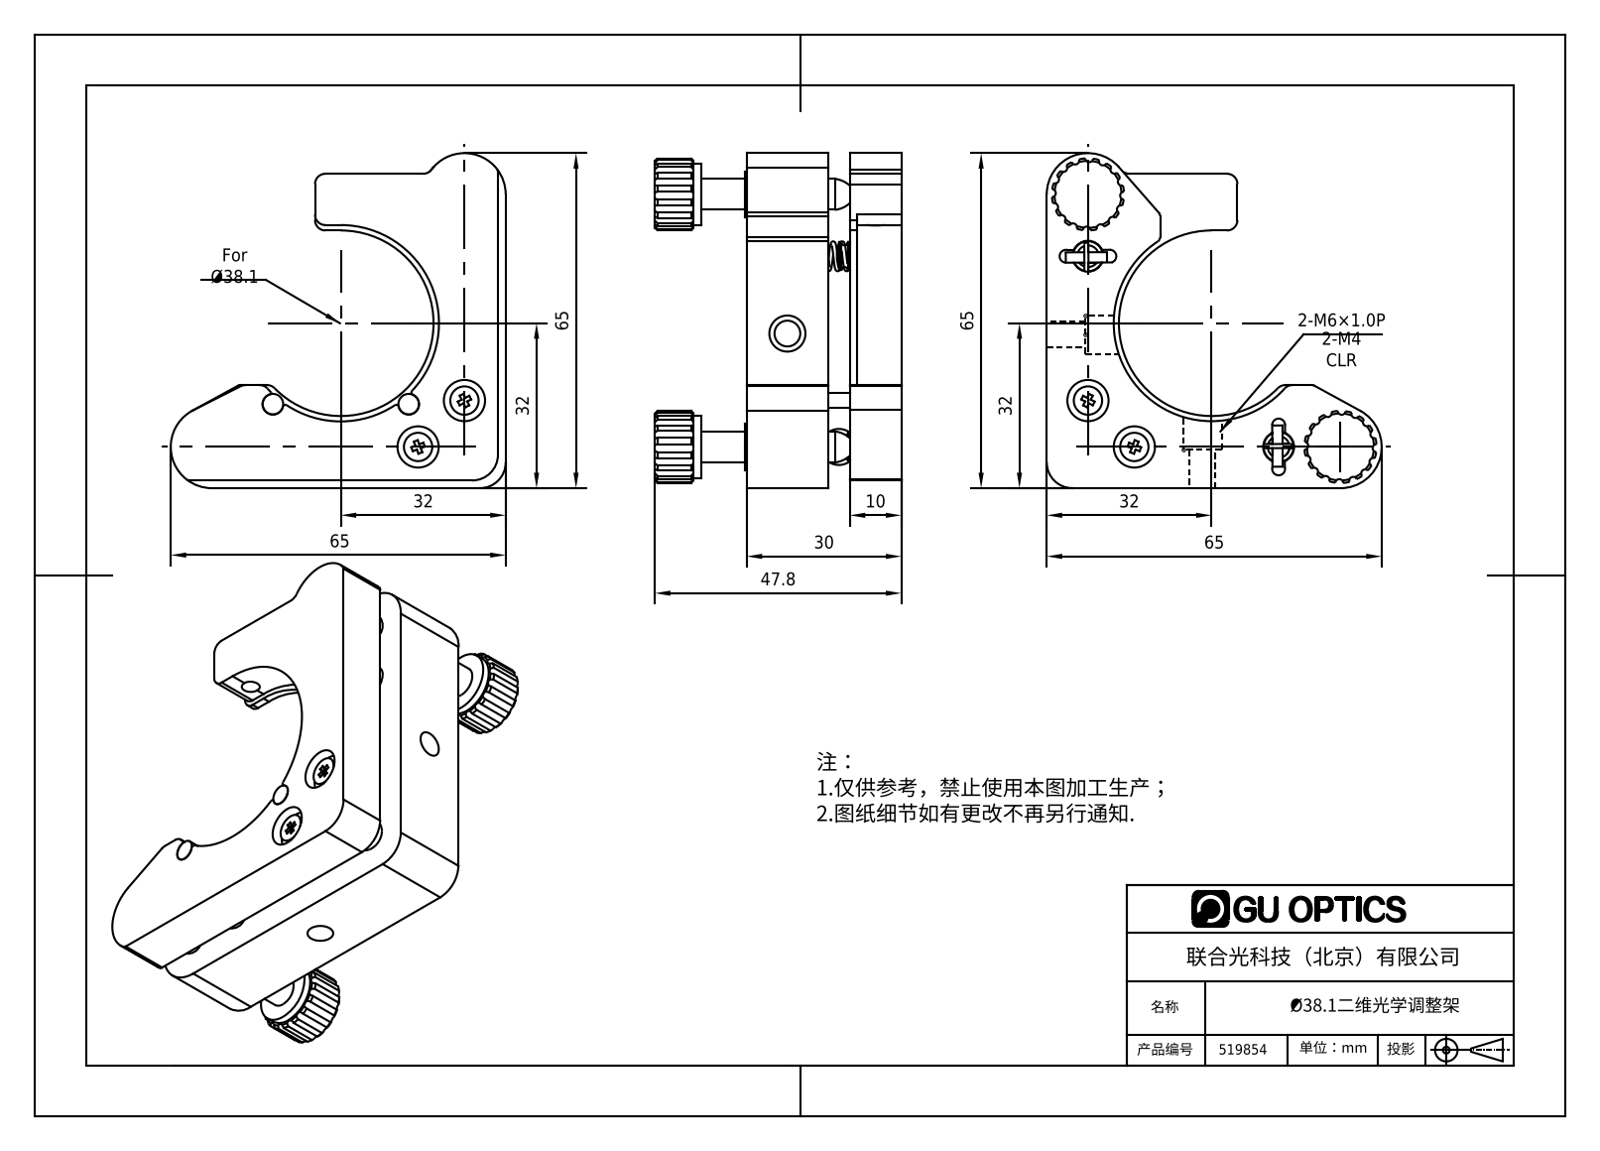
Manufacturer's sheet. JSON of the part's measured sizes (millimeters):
{"part_name": "519854", "step_written_by": "SolidWorks 2016 (AUTOMOTIVE_DESIGN)", "units": "millimeters", "bodies": {"solids": 0, "faces": 628, "planar": 220, "cylindrical": 203, "other": 205}, "overall_size": [65, 65, 47.8], "round_holes": [[6, 4], [8, 4], [4, 3], [5, 2], [7, 2], [3.5, 1]], "round_bosses_or_shafts": [[12, 2], [9, 2], [5.4, 2], [3, 2], [2, 2], [0.8, 2], [4, 1]], "partial_cylinders_radius": [[0.75, 32], [2, 8], [1, 5], [1.25, 4], [0.5, 3], [5, 2], [7, 2], [8, 2]], "face_to_face_distances": [20, 10, 4.2, 14.2, 30, 15.8, 1.5, 37.8, 30.3, 8.5], "hole_center_spacings": [12, 28, 38.08, 40, 49.82, 61.4, 8.3, 12.73]}
